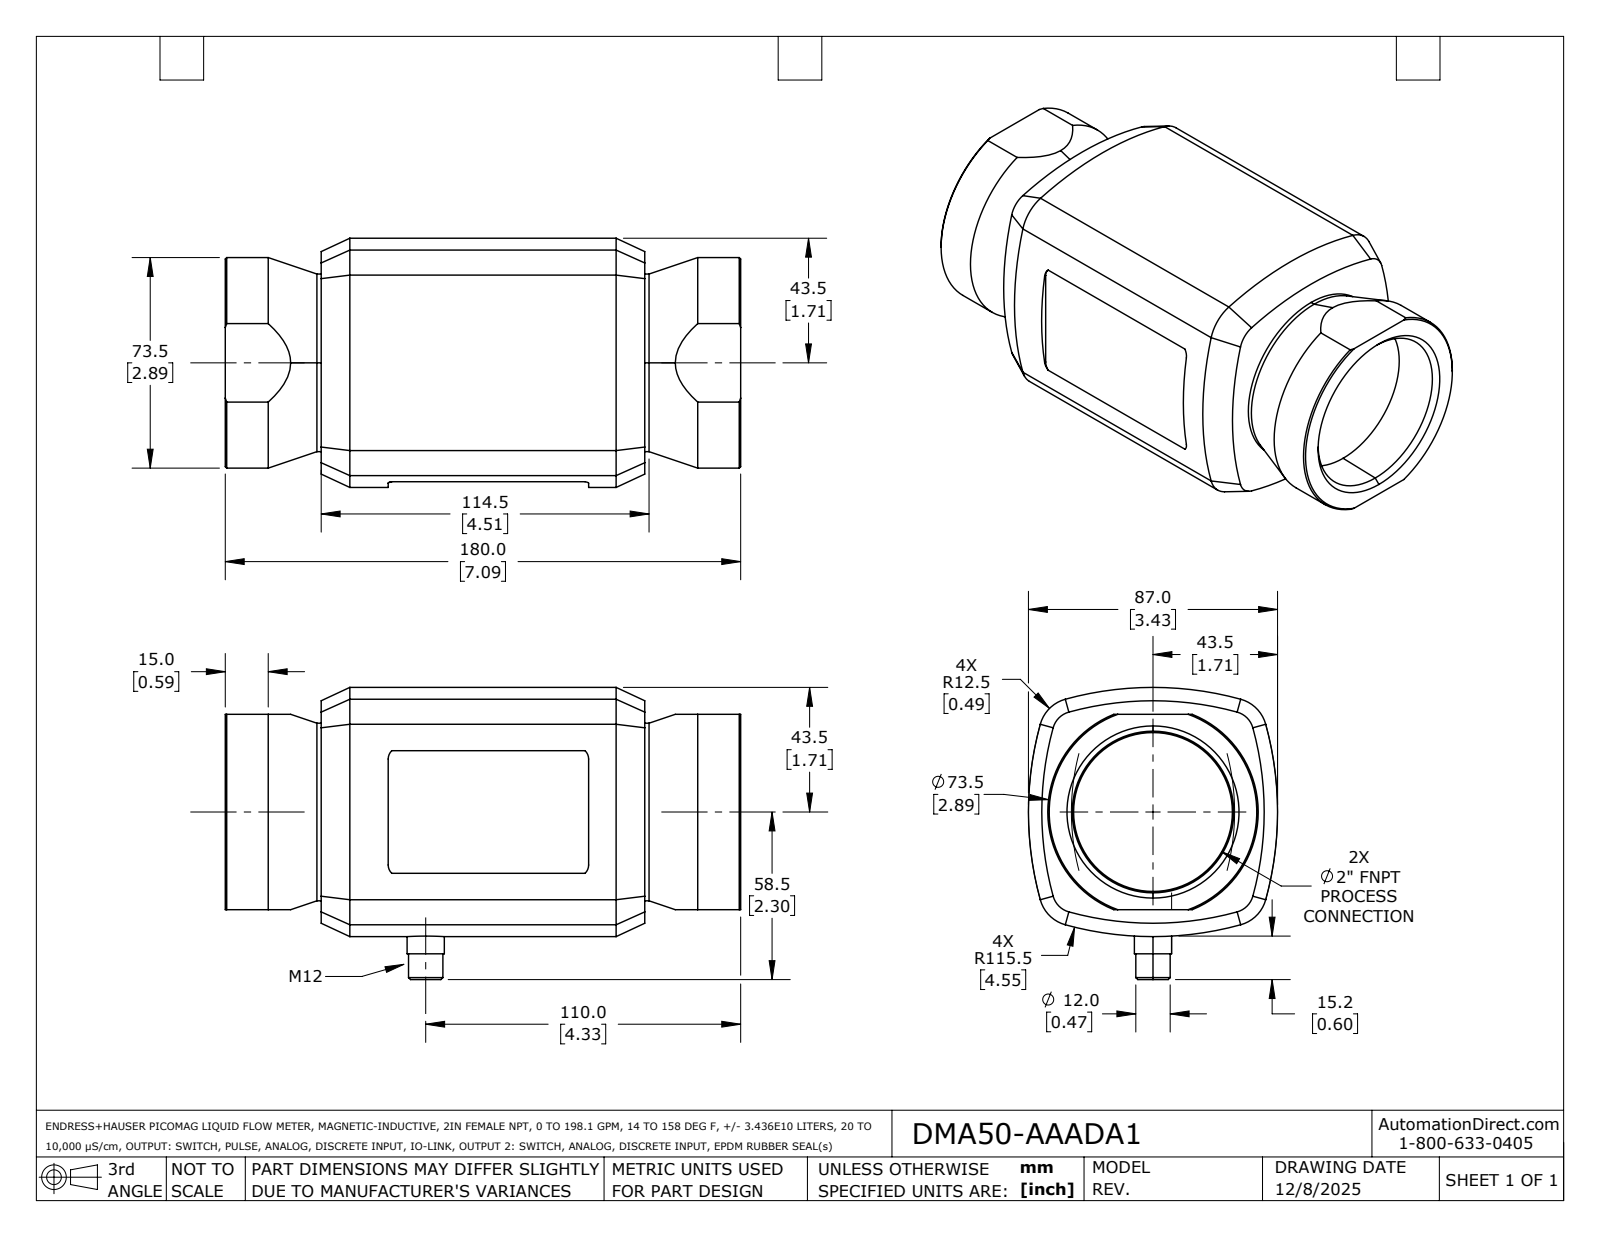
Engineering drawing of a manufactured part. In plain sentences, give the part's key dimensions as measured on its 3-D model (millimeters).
The part is named "DMA50-AAADA1". Its 3-D file was written by "SolidWorks 2024 (AUTOMOTIVE_DESIGN)". It is 1 solid with 76 faces: 16 planar, 26 cylindrical and 34 other. Overall it measures 180 by 102 by 87 millimeters. Its volume is 917 482 cubic millimeters and its surface area 68 878 square millimeters. Round holes: 1 of diameter 9.7. Round bosses or shafts: 1 of diameter 62, 1 of diameter 13, 1 of diameter 12. Partial cylindrical surfaces (rounded edges, fillets, slot ends): 4 of radius 4, 4 of radius 12.5, 4 of radius 115.5, 1 of radius 36.75. The main face-to-face distances are 15.8, 128.8, 17.7, 33.5, 146.5, 162.3, 113, 144.6, 180, 68.2.
